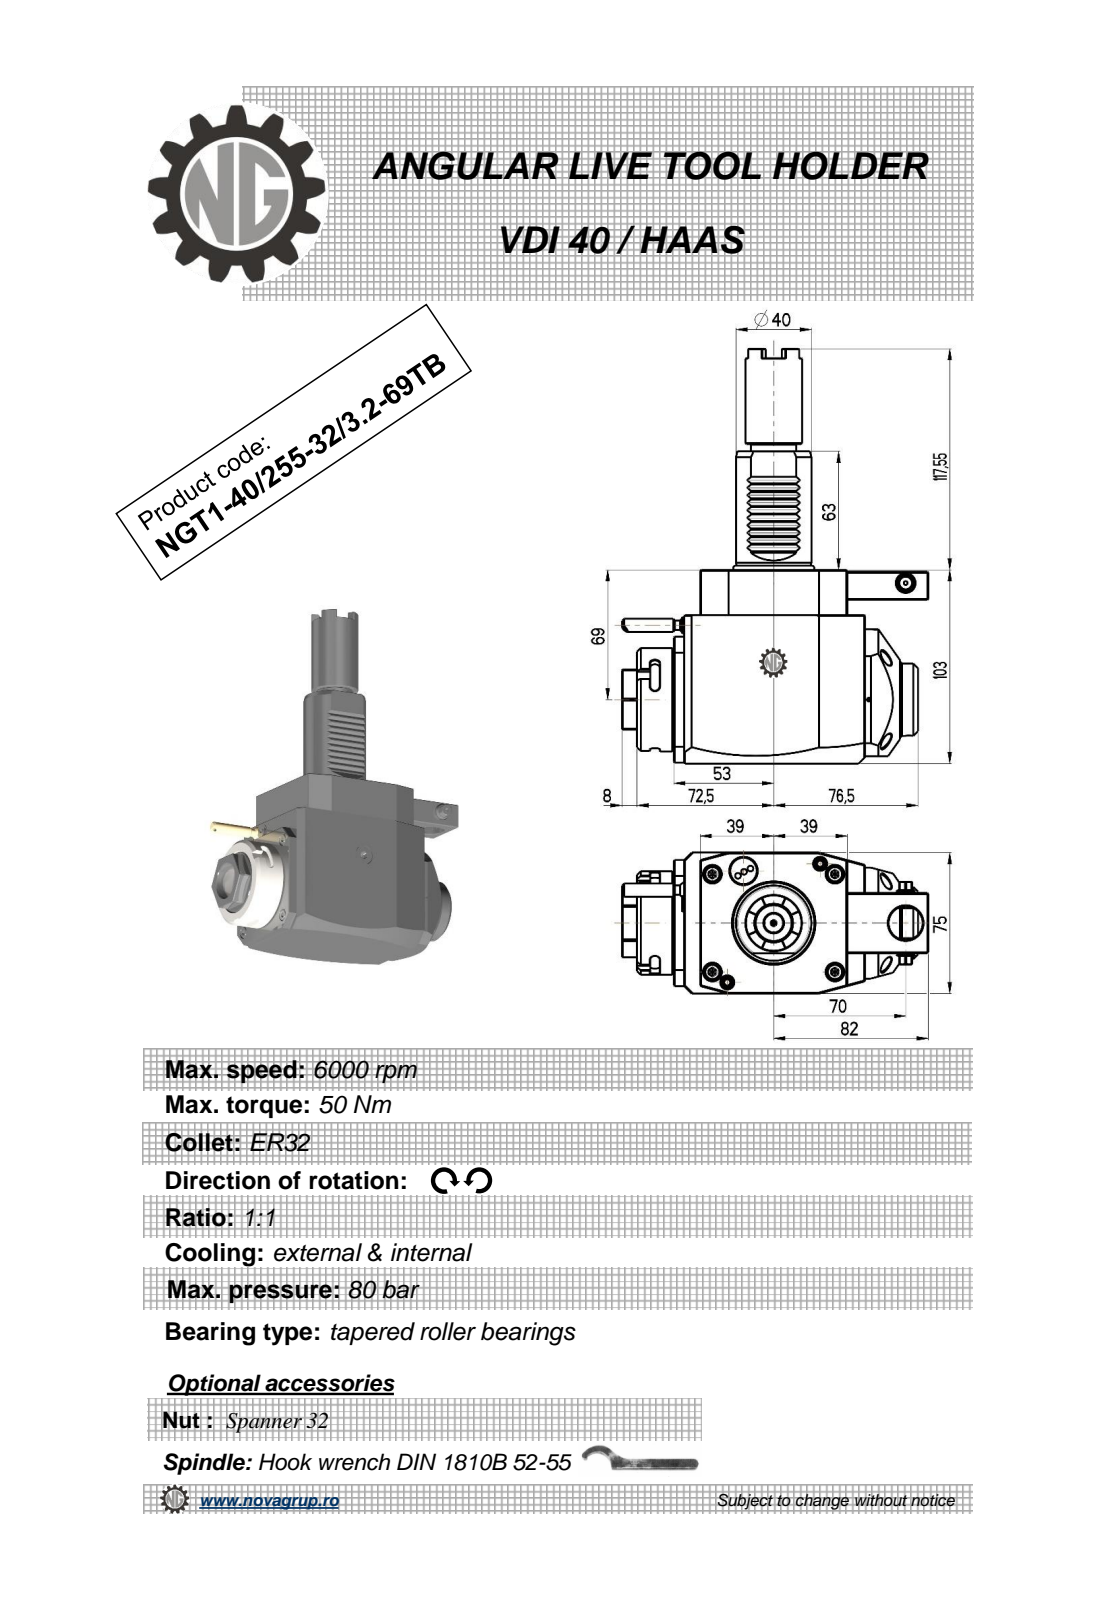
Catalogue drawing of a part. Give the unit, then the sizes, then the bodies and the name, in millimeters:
Units: millimetres
Overall size (bounding box): 220.55 × 162.5 × 75
Round holes (diameter × count): ⌀2 ×1, ⌀2.5 ×1, ⌀3 ×1, ⌀9.5 ×1, ⌀18 ×1, ⌀20 ×1, ⌀23 ×1
Round bosses / shafts (diameter × count): ⌀8.96 ×2, ⌀55 ×1, ⌀48 ×1, ⌀40 ×1, ⌀38.5 ×1, ⌀30 ×1, ⌀24 ×1, ⌀10 ×1
Partial cylindrical surfaces — rounded edges, fillets, slot ends (radius × count): R0.3 ×10, R2.5 ×6, R180 ×2, R0.5 ×1, R3.85 ×1, R4.25 ×1, R24.5 ×1, R37.5 ×1
Main face-to-face distances: 75, 103, 33.5, 19.5, 79, 8, 14, 102, 21.5, 87
Hole centre spacings: 28.11, 43.2, 61.5, 70
Volume: 952 287 mm³ · Surface area: 76 404 mm²
Bodies: 1 solid, 397 faces (219 planar, 88 cylindrical, 90 other)
Part name (STEP PRODUCT): NGT1_40_255_32_3_2_69TB
STEP written by: PRO/ENGINEER BY PARAMETRIC TECHNOLOGY CORPORATION, 2010280 (CONFIG_CONTROL_DESIGN)
